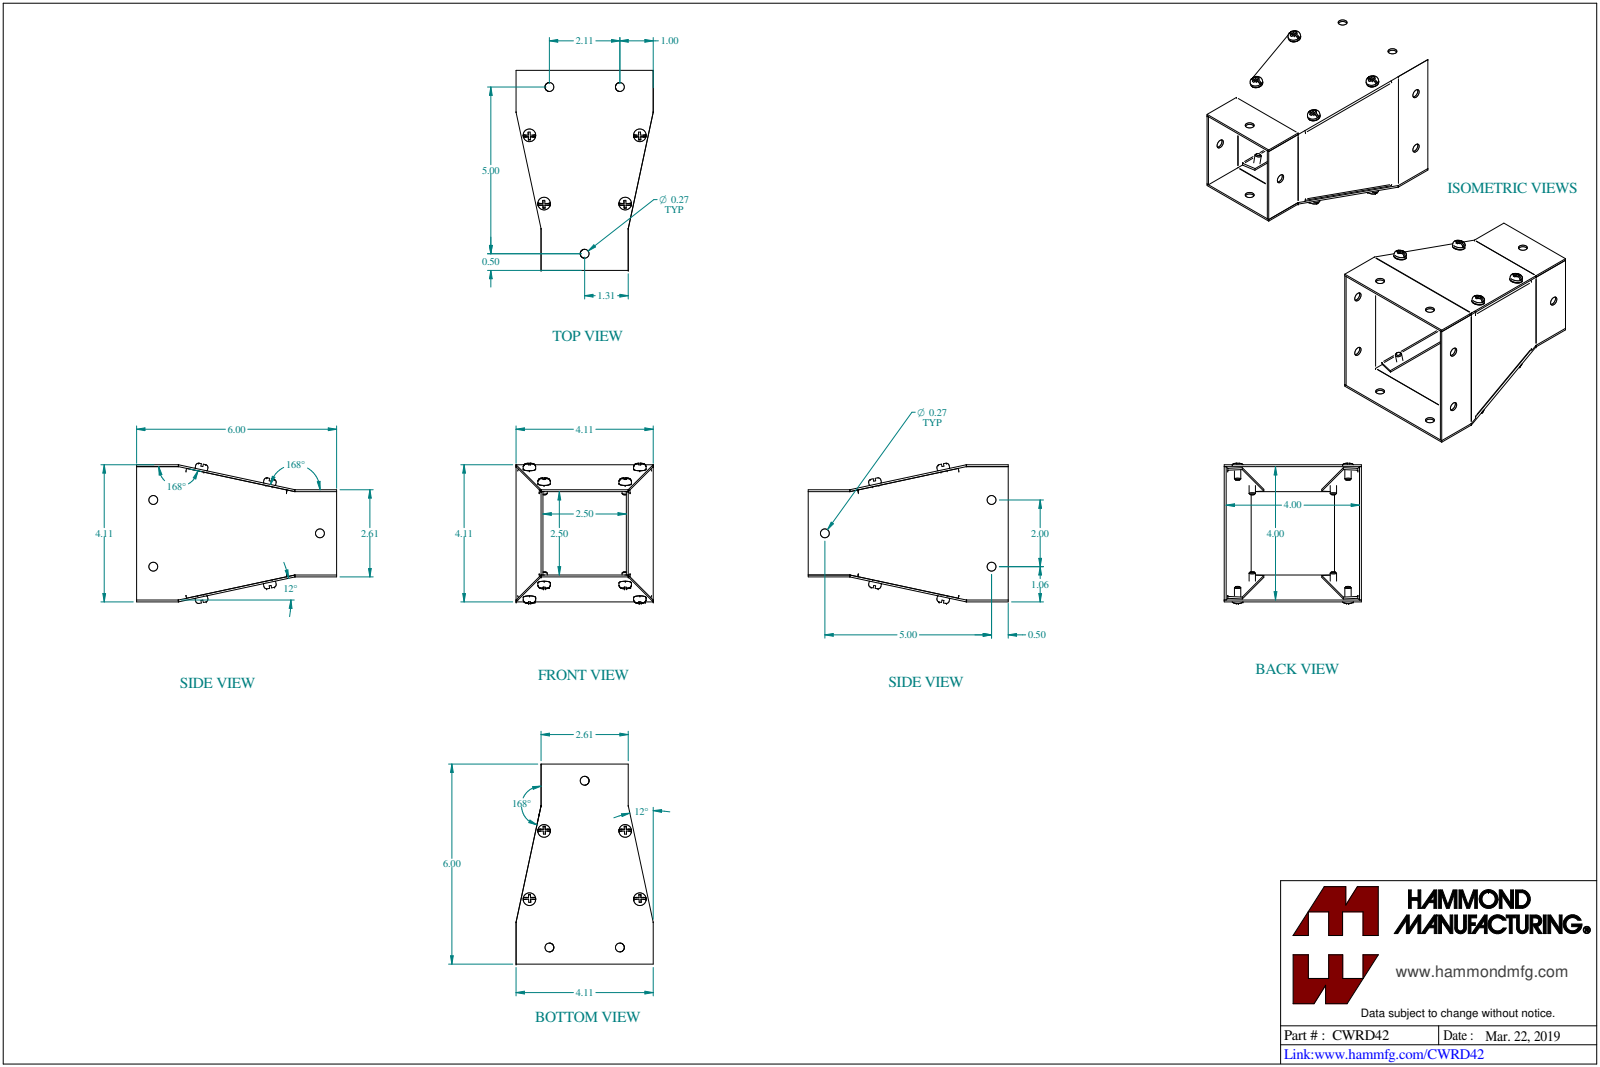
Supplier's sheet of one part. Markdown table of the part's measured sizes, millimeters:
| quantity | value |
| --- | --- |
| part name | CWRD42 |
| STEP written by | SolidWorks 2023 (CONFIG_CONTROL_DESIGN) |
| units | millimeters |
| bodies | 12 solids, 408 faces (232 planar, 112 cylindrical, 64 other) |
| overall size | 152.4 × 106.9 × 104.5 |
| volume | 82 020 mm³ |
| surface area | 115 900 mm² |
| round holes (diameter × count) | 4.3 × 8, 6.4 × 8, 6.8 × 8 |
| round bosses / shafts (diameter × count) | 9.5 × 8, 4.8 × 8 |
| partial cylindrical surfaces (radius × count) | 0.7 × 12, 2.2 × 12 |
| main face-to-face distances | 1.4, 19.1, 84, 20.5, 1.4, 103, 103, 19.1, 84, 82.6 |
| hole center spacings | 54.6, 54.4, 90.3, 90.3, 90.5, 129.8, 61.8, 84.2 |
